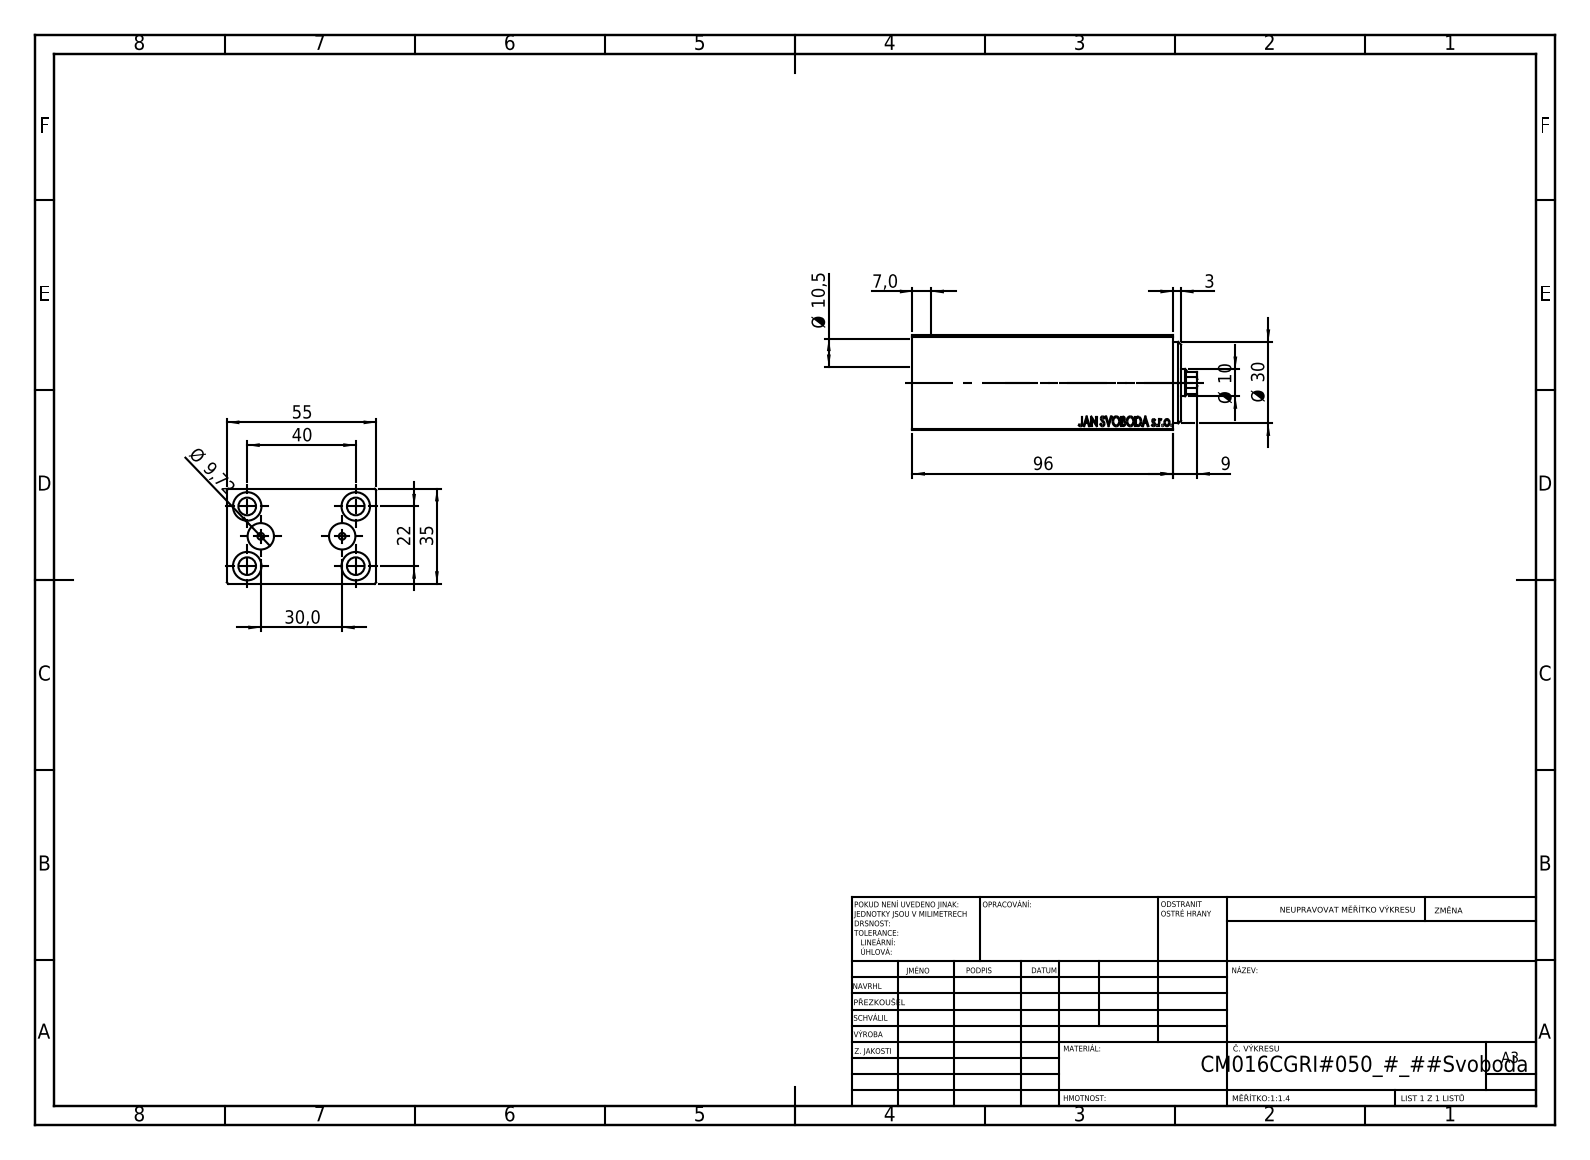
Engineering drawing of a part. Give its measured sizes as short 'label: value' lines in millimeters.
name: V450CM_VC_B; V450CM_C_Body; V450CM_C_VCP
written by: SolidWorks 2019 (CONFIG_CONTROL_DESIGN)
unit: mm
bodies: 3 solids, 861 faces (409 planar, 58 cylindrical, 394 other)
size: 105 × 55 × 35
volume: 162 712 mm³; area: 42 937 mm²
holes: 4× ⌀6.5, 4× ⌀10.5, 2× ⌀2.5, 2× ⌀9.72, 1× ⌀4.5, 1× ⌀10, 1× ⌀13.5, 1× ⌀14.5, 1× ⌀16, 1× ⌀18, 1× ⌀30
rounds: 1× R4.5
face distances: 35, 55, 5, 91, 96, 2, 3, 89, 86, 8
hole spacings: 12.08, 22.83, 36.69, 15, 22, 40, 45.65, 30
